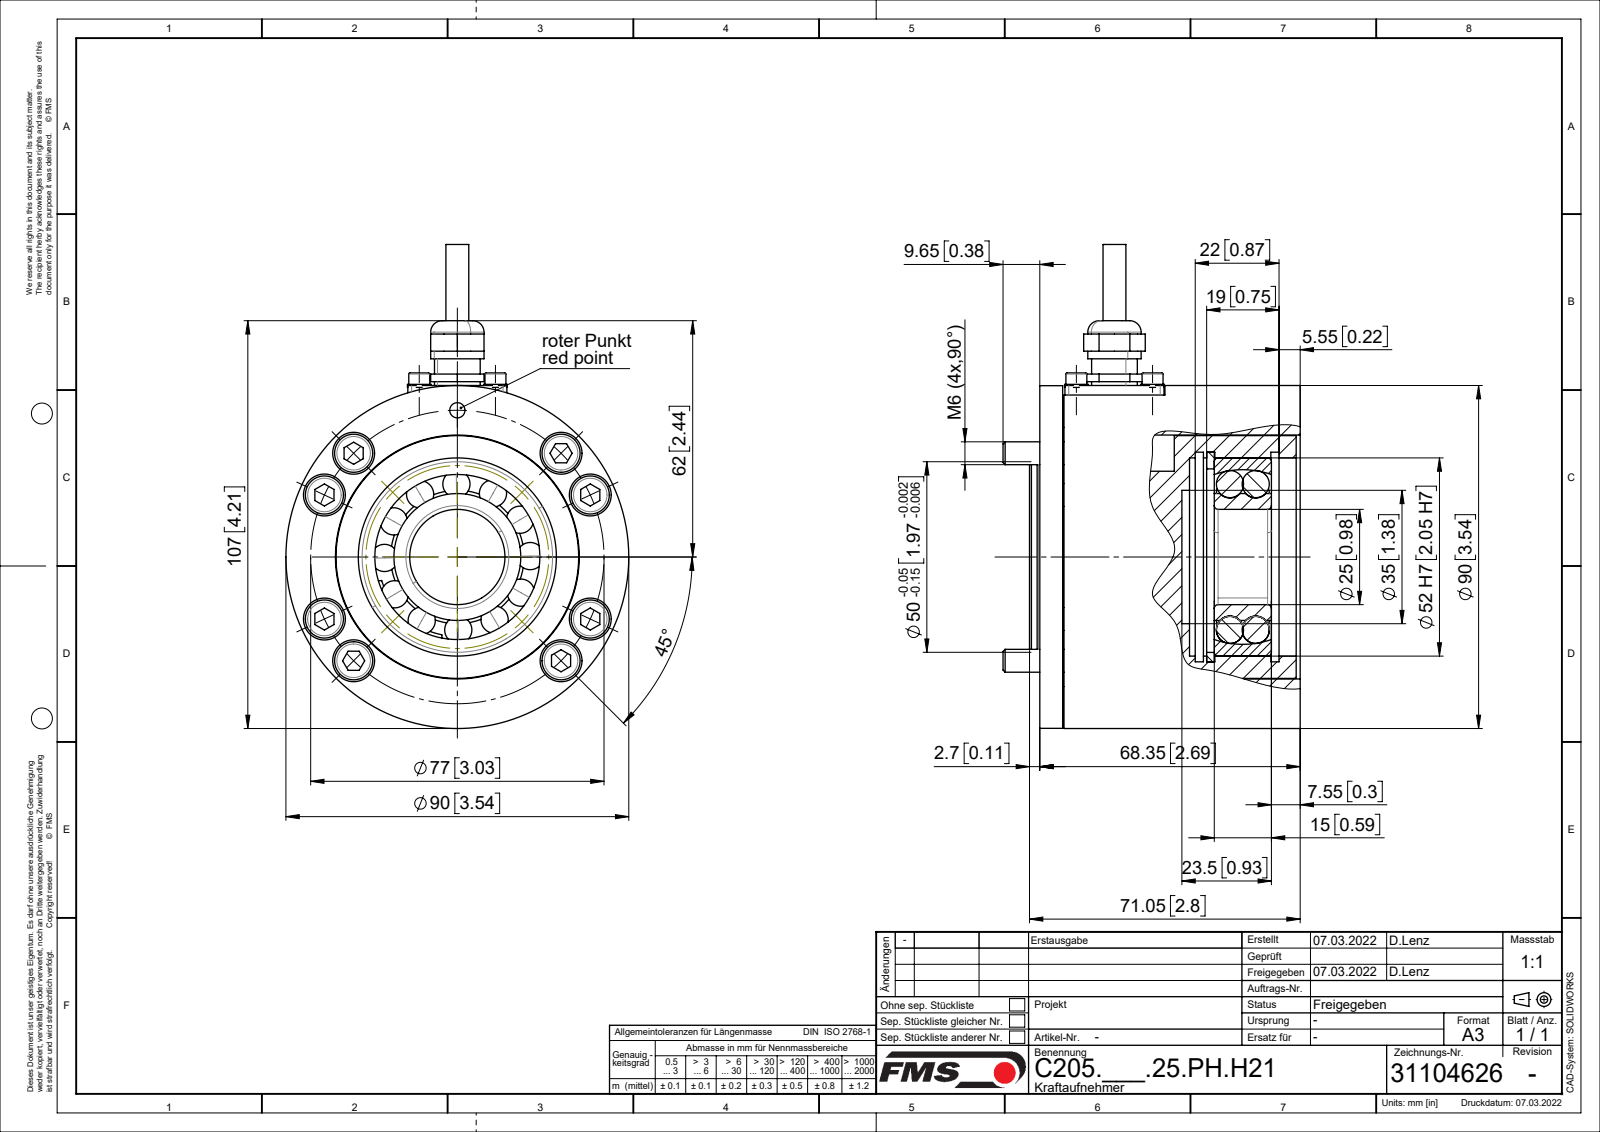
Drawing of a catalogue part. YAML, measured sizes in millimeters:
part_name: "Si-Ring DIN472_D52x2; 31104626; 31104502_01; Zyl-Schr DIN912_M6x30 (+8 more)"
step_written_by: "SolidWorks 2018 (CONFIG_CONTROL_DESIGN)"
units: millimeters
bodies: {solids: 49, faces: 608, planar: 222, cylindrical: 234, other: 152}
overall_size: [127, 90, 78]
volume: 298818
surface_area: 121022
round_holes:
  - {diameter: 6.5, count: 8}
  - {diameter: 11, count: 8}
  - {diameter: 2.5, count: 6}
  - {diameter: 3.1, count: 4}
  - {diameter: 3.4, count: 4}
  - {diameter: 5, count: 4}
  - {diameter: 7, count: 4}
  - {diameter: 4, count: 2}
  - {diameter: 6, count: 1}
  - {diameter: 10.2, count: 1}
  - {diameter: 12.2, count: 1}
  - {diameter: 18, count: 1}
round_bosses_or_shafts:
  - {diameter: 10, count: 8}
  - {diameter: 6, count: 8}
  - {diameter: 6.2, count: 4}
  - {diameter: 5.5, count: 4}
  - {diameter: 3, count: 4}
  - {diameter: 90, count: 1}
  - {diameter: 89.9, count: 1}
  - {diameter: 63.7, count: 1}
partial_cylinders:
  - {radius: 0.1, count: 4}
  - {radius: 1, count: 4}
  - {radius: 4.24, count: 2}
  - {radius: 5, count: 2}
  - {radius: 20.8, count: 1}
  - {radius: 24.1, count: 1}
face_to_face_distances: [6, 3.3, 2.7, 6.5, 32, 33.05, 2, 38, 29.3, 35.3]
hole_center_spacings: [20, 38.5, 13.37, 14.14, 38.49, 44.16, 54.44, 63.07]
